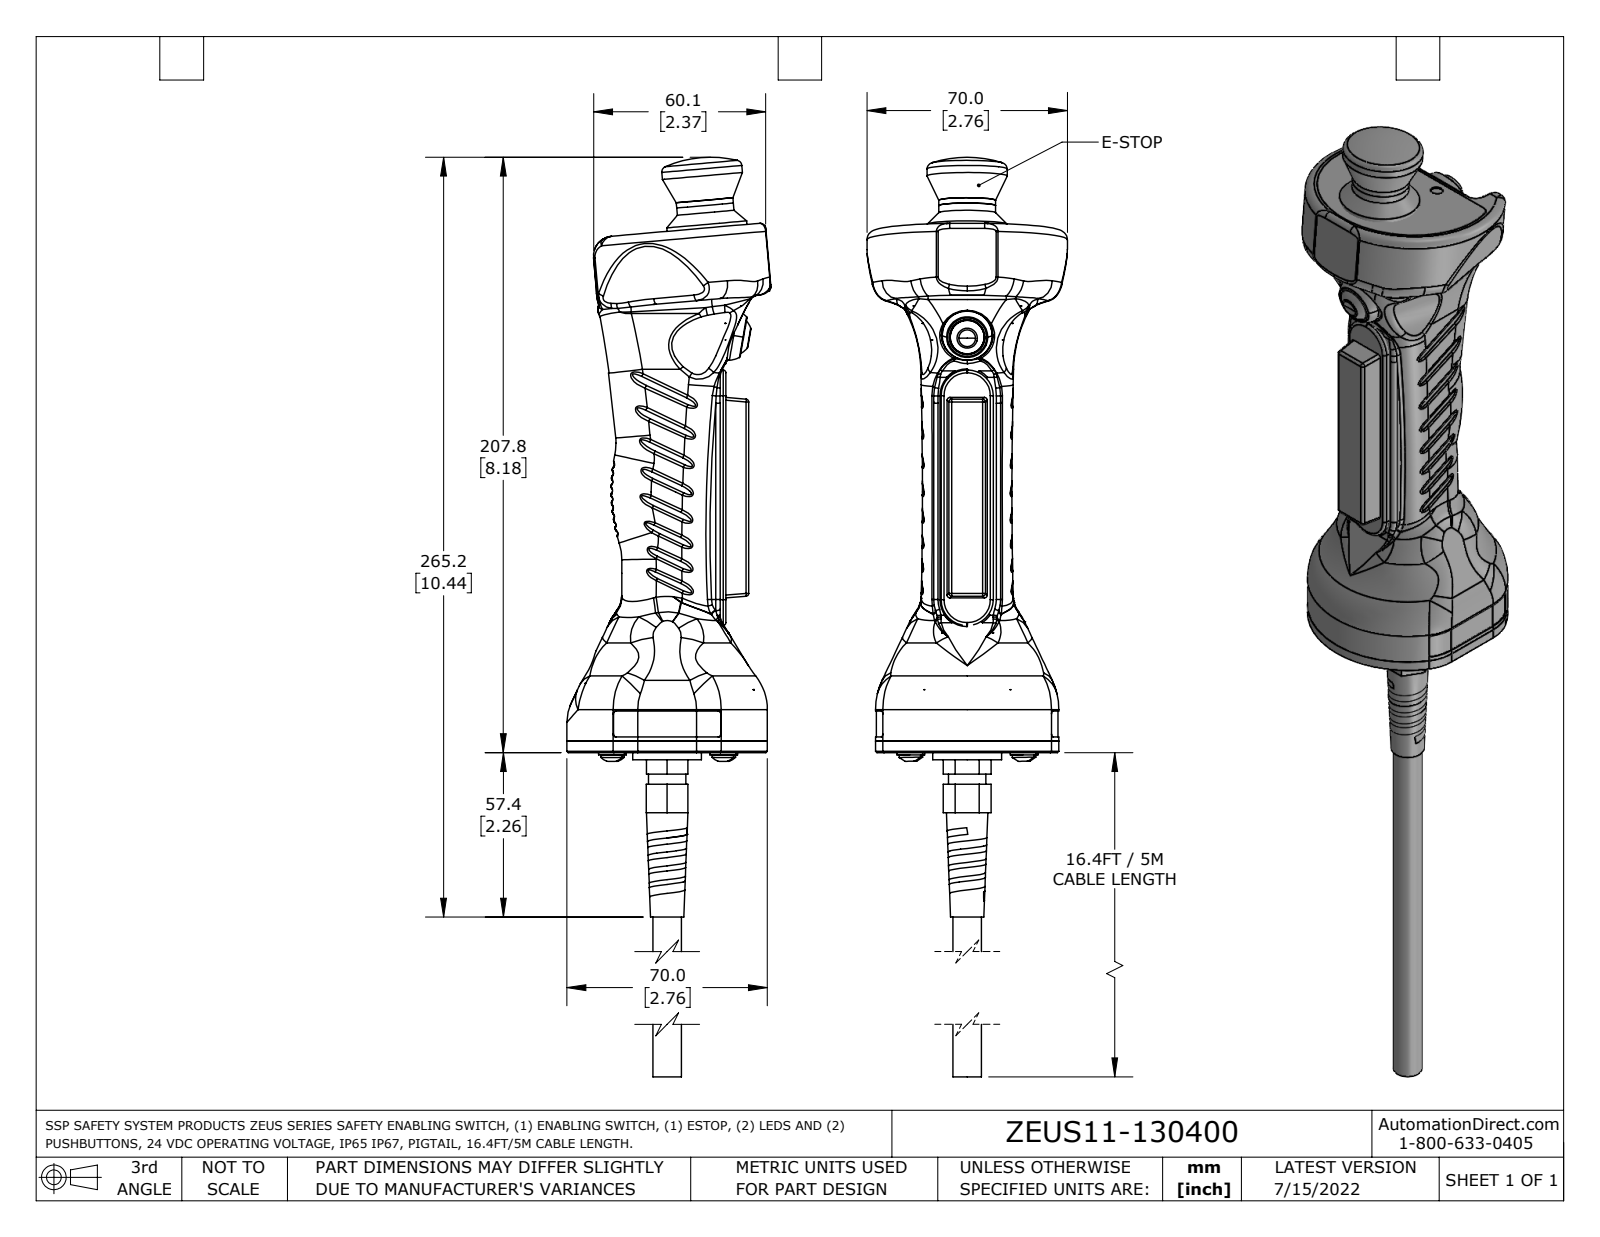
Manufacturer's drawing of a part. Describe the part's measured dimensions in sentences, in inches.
The part is named "ZEUS11-130400". Its 3-D file was written by "SolidWorks 2021 (AUTOMOTIVE_DESIGN)". It is 21 solids with 1624 faces: 623 planar, 518 cylindrical and 483 other. Overall it measures 15.833 by 2.803 by 2.756 inches. Its volume is 22.86 cubic inches and its surface area 140 square inches. Round holes: 4 of diameter 0.132, 4 of diameter 0.169, 4 of diameter 0.177, 4 of diameter 0.197, 2 of diameter 0.039, 2 of diameter 0.098, 2 of diameter 0.11, 2 of diameter 0.159, 2 of diameter 0.165, 2 of diameter 0.173, 2 of diameter 0.201, 2 of diameter 0.205. Round bosses or shafts: 4 of diameter 0.354, 4 of diameter 0.295, 4 of diameter 0.157, 4 of diameter 0.039, 3 of diameter 0.461, 2 of diameter 1.102, 2 of diameter 0.781, 2 of diameter 0.689. Partial cylindrical surfaces (rounded edges, fillets, slot ends): 96 of radius 0.005, 51 of radius 0.039, 48 of radius 0.028, 42 of radius 0.008, 21 of radius 0.079, 16 of radius 0.006, 10 of radius 0.118, 7 of radius 0.031. The main face-to-face distances are 0.157, 0.079, 0.02, 0.014, 0.065, 0.059, 0.098, 0.039, 0.177, 0.571. The hole center spacings are 0.404, 0.63, 0.867, 1.08, 1.181, 1.531, 1.558, 0.513.
